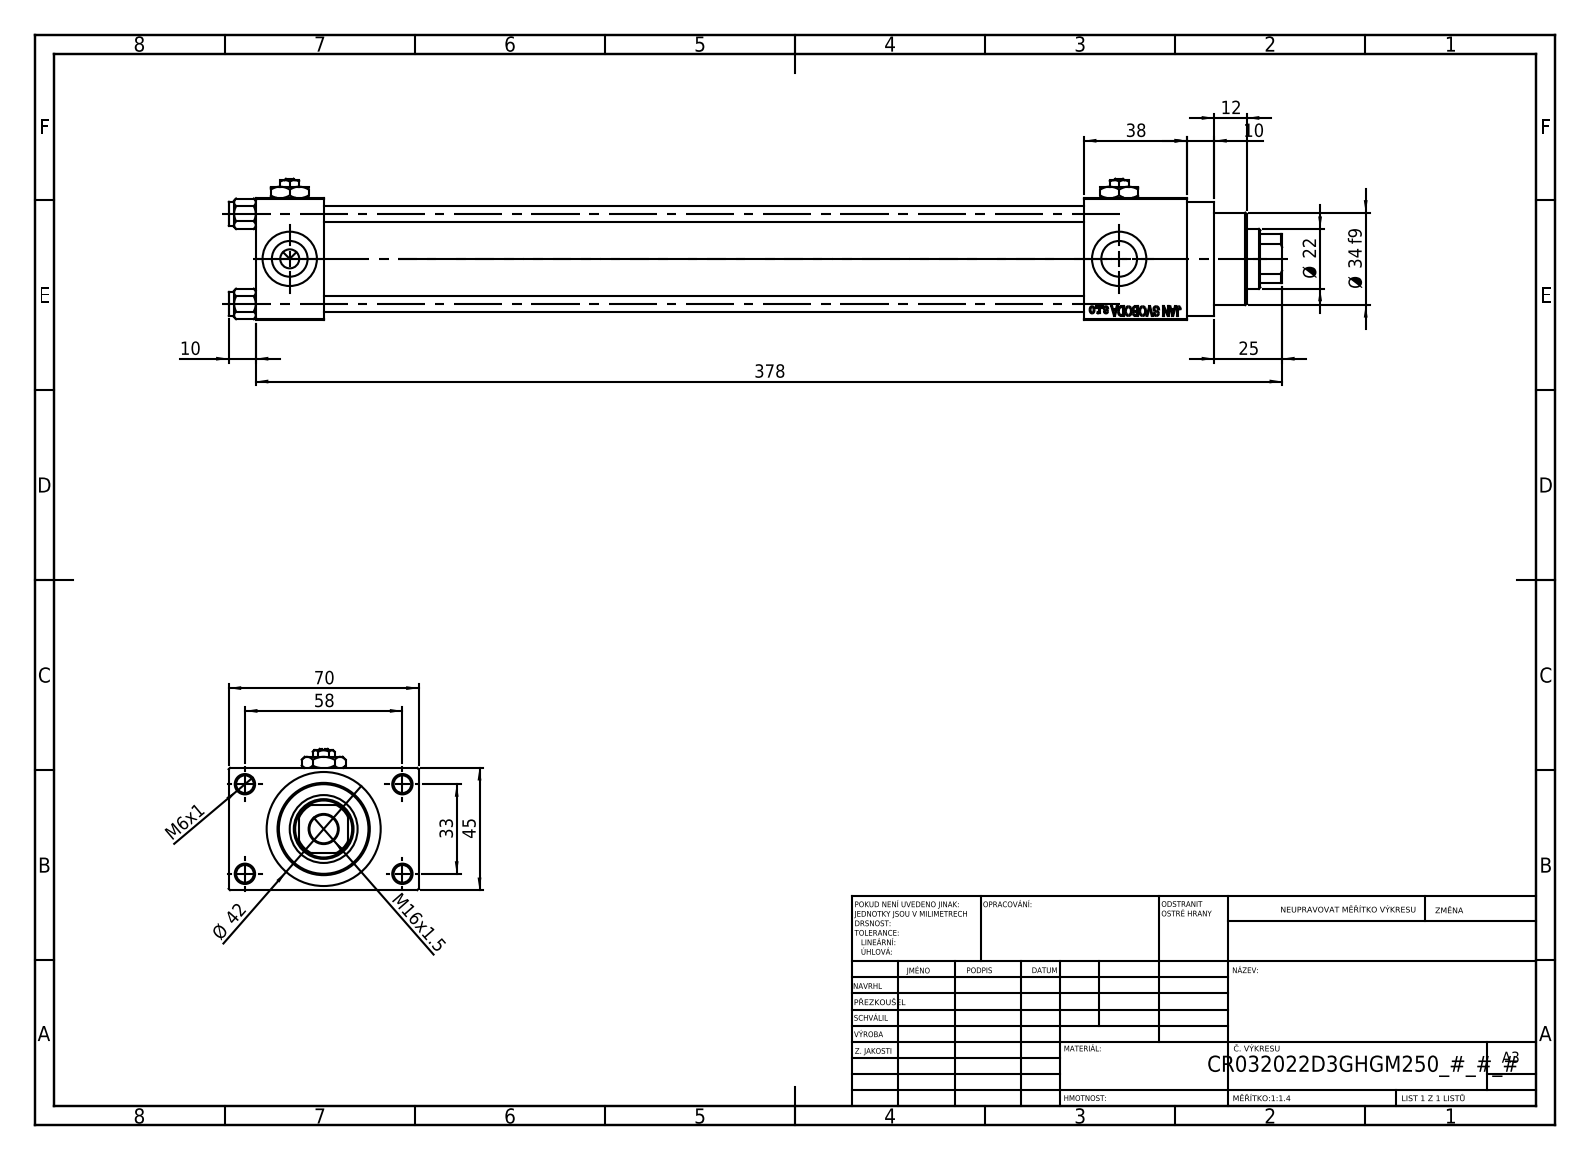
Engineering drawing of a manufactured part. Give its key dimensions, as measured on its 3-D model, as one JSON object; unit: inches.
{"part_name": "V215CR_VCP_D; NUT_M5_D; V215CR_D_TYCINKA; Zatka_pro_OIL_PORT (+2 more)", "step_written_by": "SolidWorks 2019 (CONFIG_CONTROL_DESIGN)", "units": "inches", "bodies": {"solids": 13, "faces": 1201, "planar": 542, "cylindrical": 99, "other": 560}, "overall_size": [15.276, 2.756, 2.047], "volume_in3": 26.3, "surface_area_in2": 256.6, "round_holes": [[0.236, 4], [0.256, 4], [0.518, 4], [0.787, 4], [0.276, 3], [0.413, 1], [0.866, 1], [0.945, 1], [0.984, 1], [1.26, 1], [1.299, 1]], "round_bosses_or_shafts": [[0.354, 4], [1.654, 1], [1.496, 1], [1.339, 1]], "partial_cylinders_radius": [[0.413, 1]], "face_to_face_distances": [1.772, 0.984, 0.492, 11.024, 12.008, 2.264, 12.52, 1.496, 13.504, 2.756], "hole_center_spacings": [0.488, 0.924, 1.307, 1.314, 1.392, 1.795, 2.219, 1.299]}
